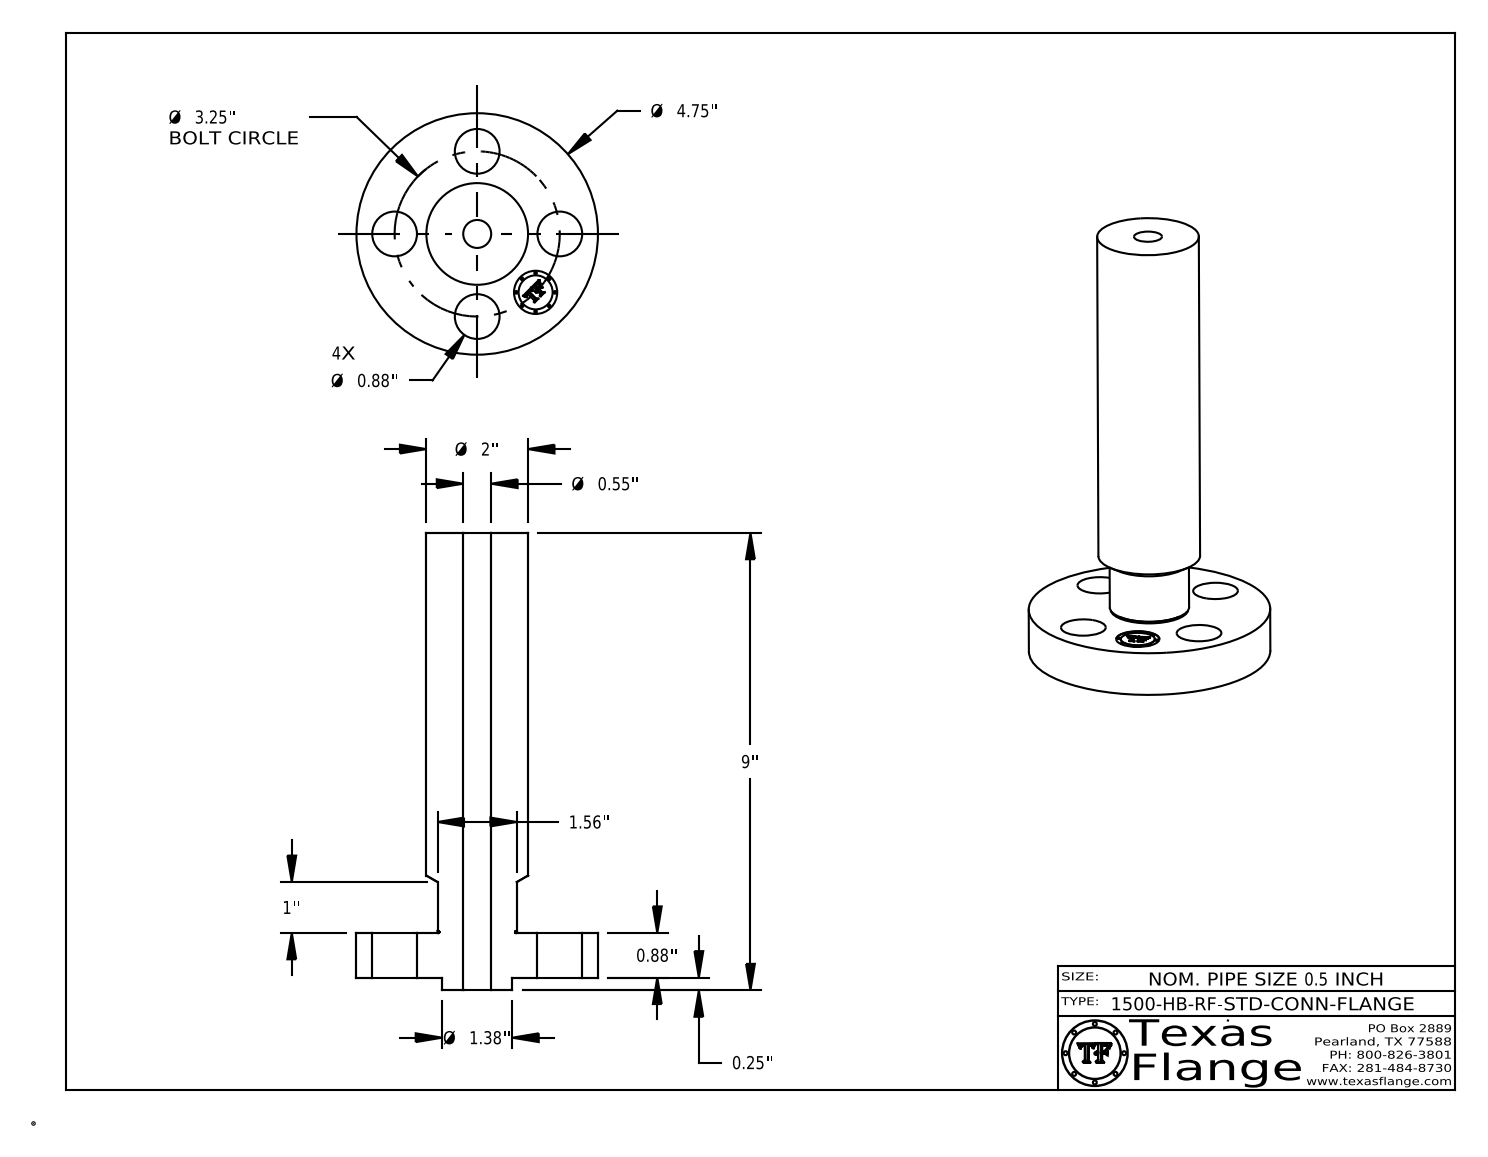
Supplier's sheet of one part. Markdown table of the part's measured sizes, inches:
| quantity | value |
| --- | --- |
| part name | 0.5-1500-HB-RF-STD-CONN-FLANGE |
| STEP written by | CATIA V5 STEP AP214 (AUTOMOTIVE_DESIGN) |
| units | inches |
| bodies | 1 solid, 413 faces (369 planar, 38 cylindrical, 6 other) |
| overall size | 9 × 4.75 × 4.75 |
| volume | 35.1 in³ |
| surface area | 119.8 in² |
| round holes (diameter × count) | 0.88 × 4, 0.55 × 1, 0.85 × 1 |
| round bosses / shafts (diameter × count) | 0.051 × 8, 4.75 × 1, 2 × 1, 1.56 × 1, 1.38 × 1, 0.67 × 1 |
| main face-to-face distances | 0.88, 8.75, 7.87, 0.25, 1.13, 9, 1.125, 0.875, 7.875, 0.254 |
| hole center spacings | 1.625, 2.298, 1.244, 3.003, 3.25 |
